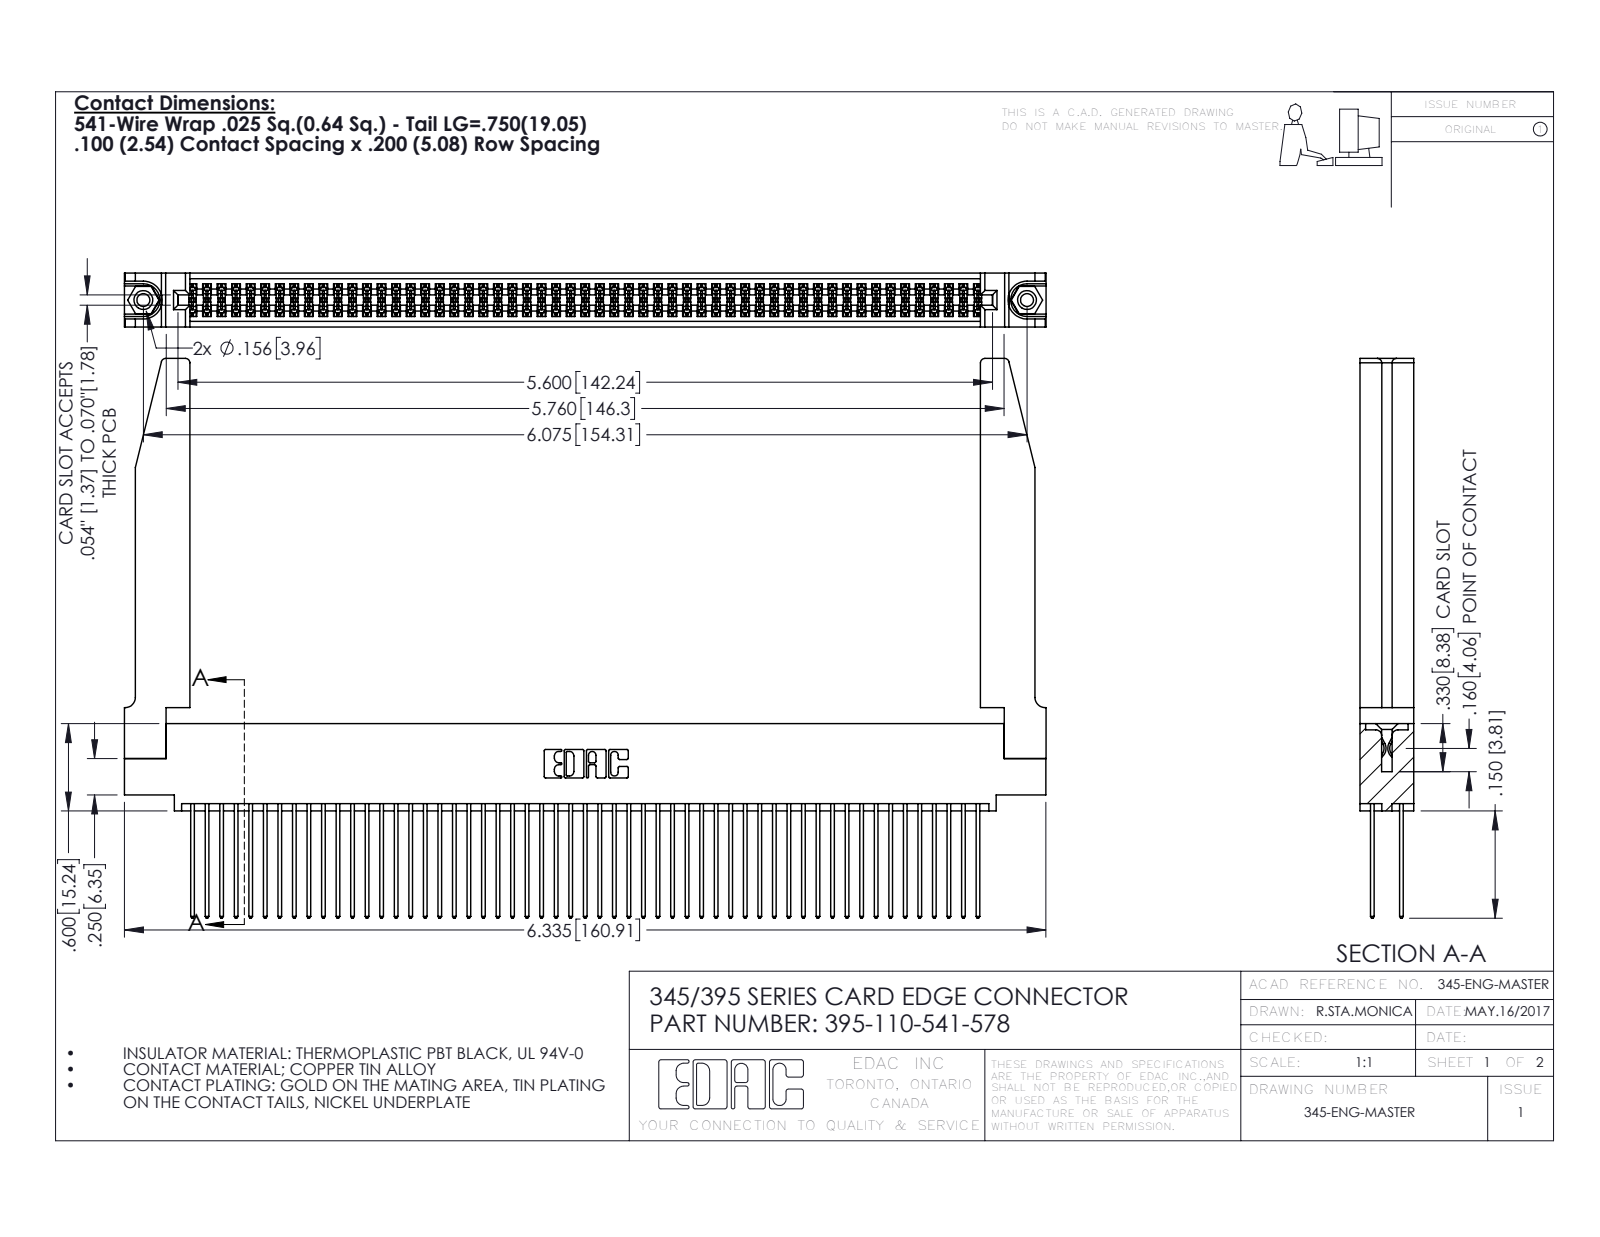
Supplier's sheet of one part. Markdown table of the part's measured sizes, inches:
| quantity | value |
| --- | --- |
| part name | 395-110-541-578; 345-292-001_345-293-141; 345 Part_0.110 Offset - 0.156 Dia-TH; 345-220-078_345-220-078 (+1 more) |
| STEP written by | SolidWorks 2016 (CONFIG_CONTROL_DESIGN) |
| units | inches |
| bodies | 115 solids, 5864 faces (3856 planar, 1956 cylindrical, 52 other) |
| overall size | 6.336 × 3.847 × 0.37 |
| volume | 1.47 in³ |
| surface area | 53.1 in² |
| round holes (diameter × count) | 0.089 × 2, 0.125 × 2, 0.156 × 2, 0.064 × 1 |
| round bosses / shafts (diameter × count) | 0.155 × 2 |
| partial cylindrical surfaces (radius × count) | 0.006 × 165, 0.01 × 110, 0.01 × 22, 0.03 × 8, 0.007 × 6, 0.031 × 6, 0.026 × 3, 0.014 × 2 |
| main face-to-face distances | 0.072, 0.298, 0.37, 0.2, 0.098, 0.272, 0.025, 0.225, 0.175, 0.148 |
| hole center spacings | 0.27, 5.839, 6.075 |
